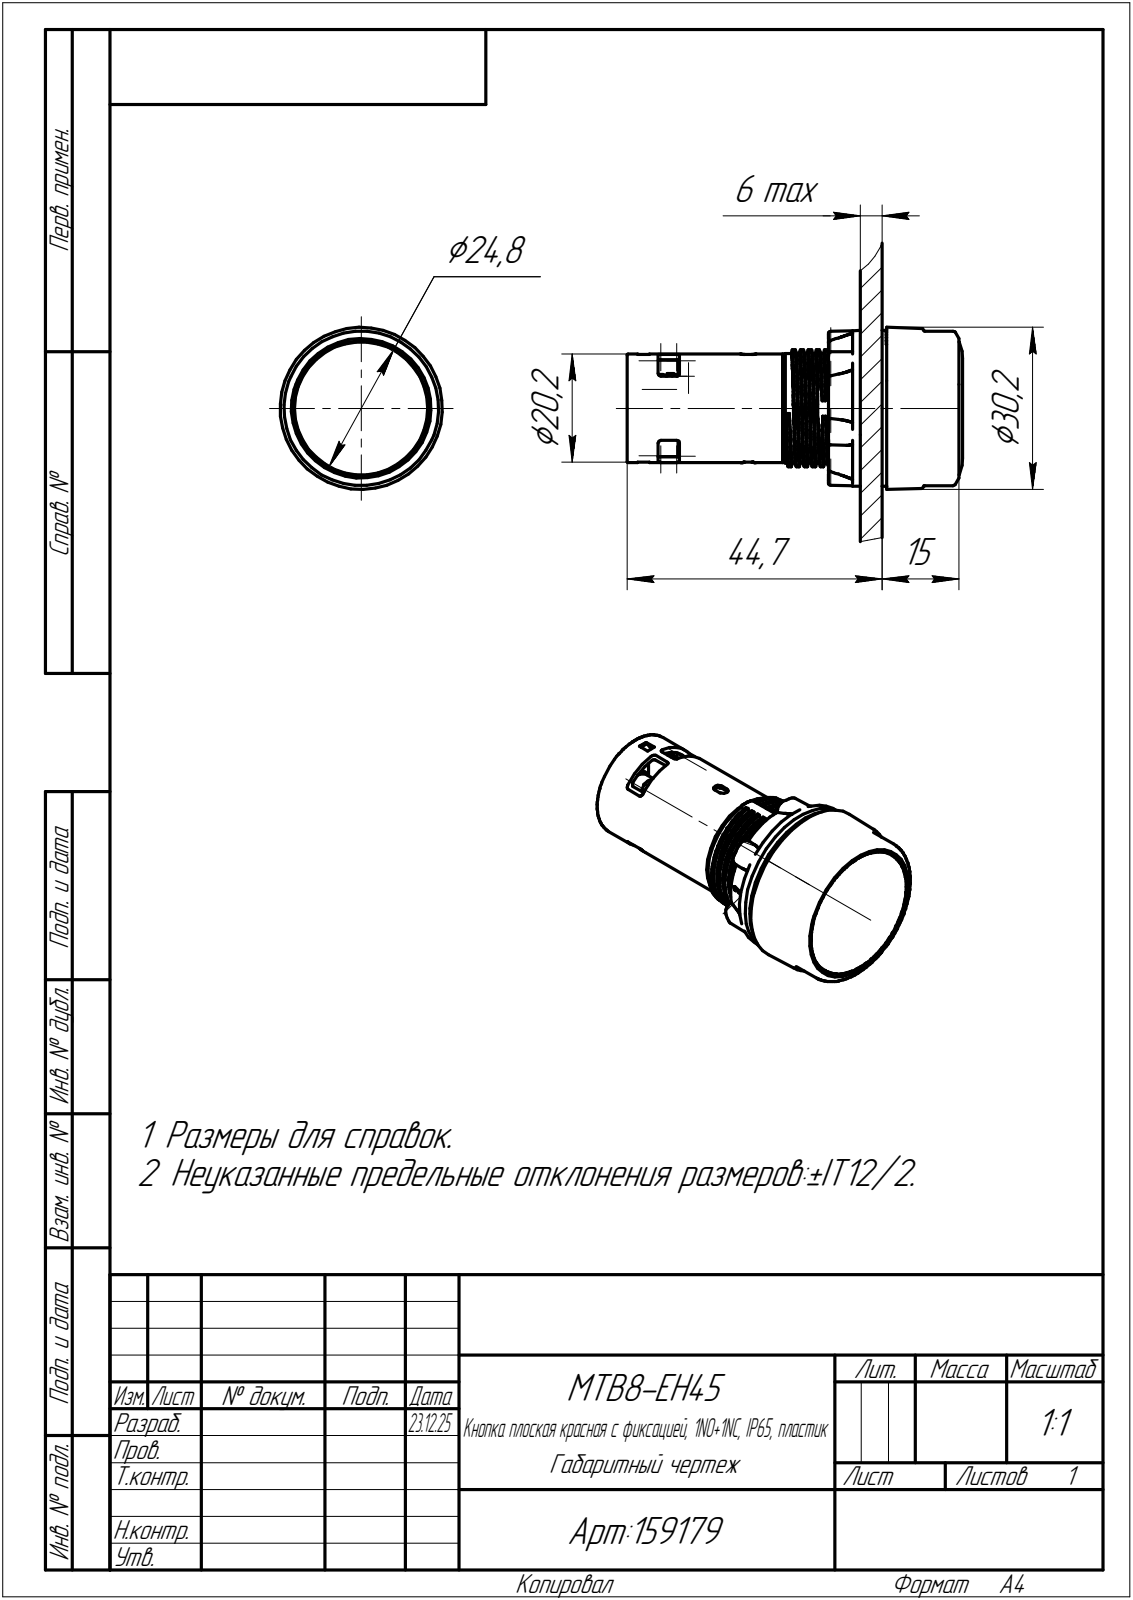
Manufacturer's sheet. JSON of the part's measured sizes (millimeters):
{"part_name": "MTB8-EH45", "step_written_by": "C3D Toolkit (CONFIG_CONTROL_DESIGN)", "units": "millimeters", "bodies": {"solids": 17, "faces": 2516, "planar": 976, "cylindrical": 755, "other": 785}, "overall_size": [59.7, 30.2, 30.2], "volume_mm3": 22520, "surface_area_mm2": 12883, "round_holes": [[2.5, 8], [2, 4], [6.2, 4], [18.1, 1], [22.4, 1], [23, 1], [23.3, 1], [25.1, 1], [28.2, 1], [29.2, 1]], "round_bosses_or_shafts": [[5.6, 4], [3.9, 4], [3, 4], [2.4, 4], [29, 1], [28.8, 1], [24.8, 1], [22, 1]], "partial_cylinders_radius": [[0.1, 180], [0.2, 40], [0.3, 36], [0.5, 28], [0.15, 27], [0.25, 8], [1.3, 8], [0.4, 7]], "face_to_face_distances": [1.2, 13.4, 1, 6, 7.2, 14.6, 12.2, 10.6, 7.6, 2.3], "hole_center_spacings": [1.56, 5.17, 5.24, 5.25, 5.66, 5.94, 6.73, 7.7]}
